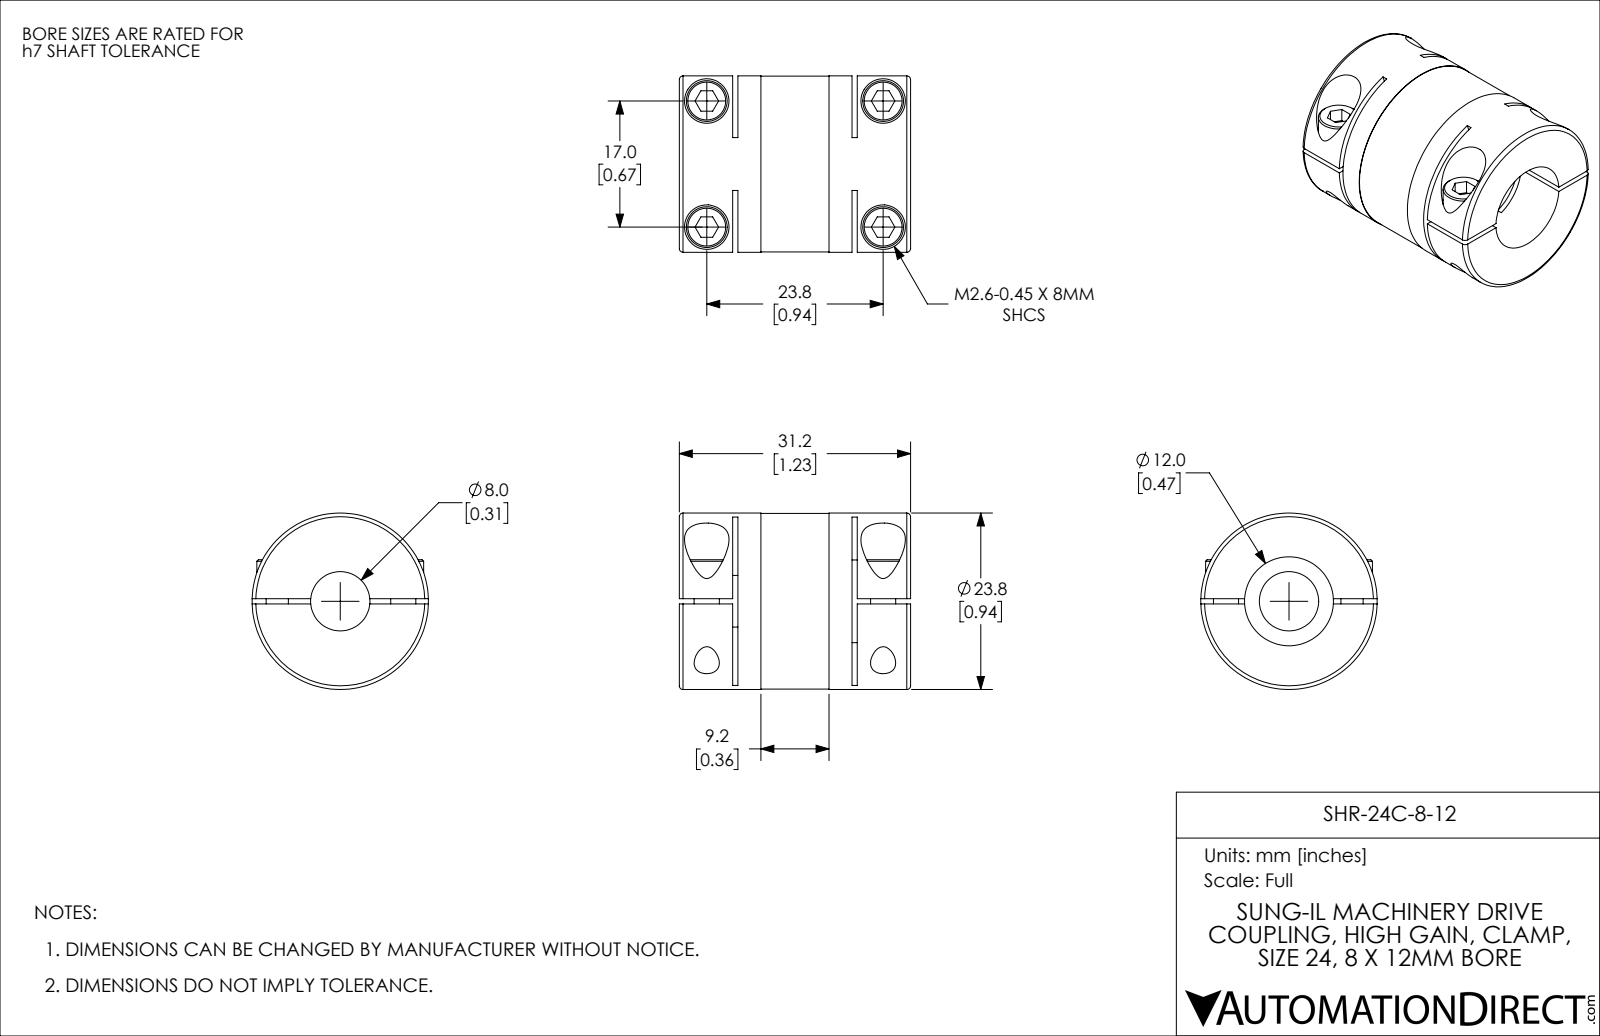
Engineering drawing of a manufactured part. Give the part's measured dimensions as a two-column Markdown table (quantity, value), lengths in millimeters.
| quantity | value |
| --- | --- |
| part name | SHR-24C-8-12 |
| STEP written by | SolidWorks 2021 (CONFIG_CONTROL_DESIGN) |
| units | millimeters |
| bodies | 1 solid, 146 faces (70 planar, 56 cylindrical, 20 other) |
| overall size | 31.2 × 23.8 × 23.8 |
| volume | 9 620 mm³ |
| surface area | 6 581 mm² |
| round holes (diameter × count) | 3.4 × 4, 6 × 4, 8 × 1, 12 × 1, 14 × 1 |
| round bosses / shafts (diameter × count) | 5.5 × 4, 3 × 2, 23.8 × 1, 23.7 × 1 |
| partial cylindrical surfaces (radius × count) | 37.5 × 2 |
| main face-to-face distances | 0.7, 7.9, 7.2, 23.3, 24, 16.1, 31.2, 15.4, 16.8, 11 |
| hole center spacings | 17, 23.8, 29.3 |
